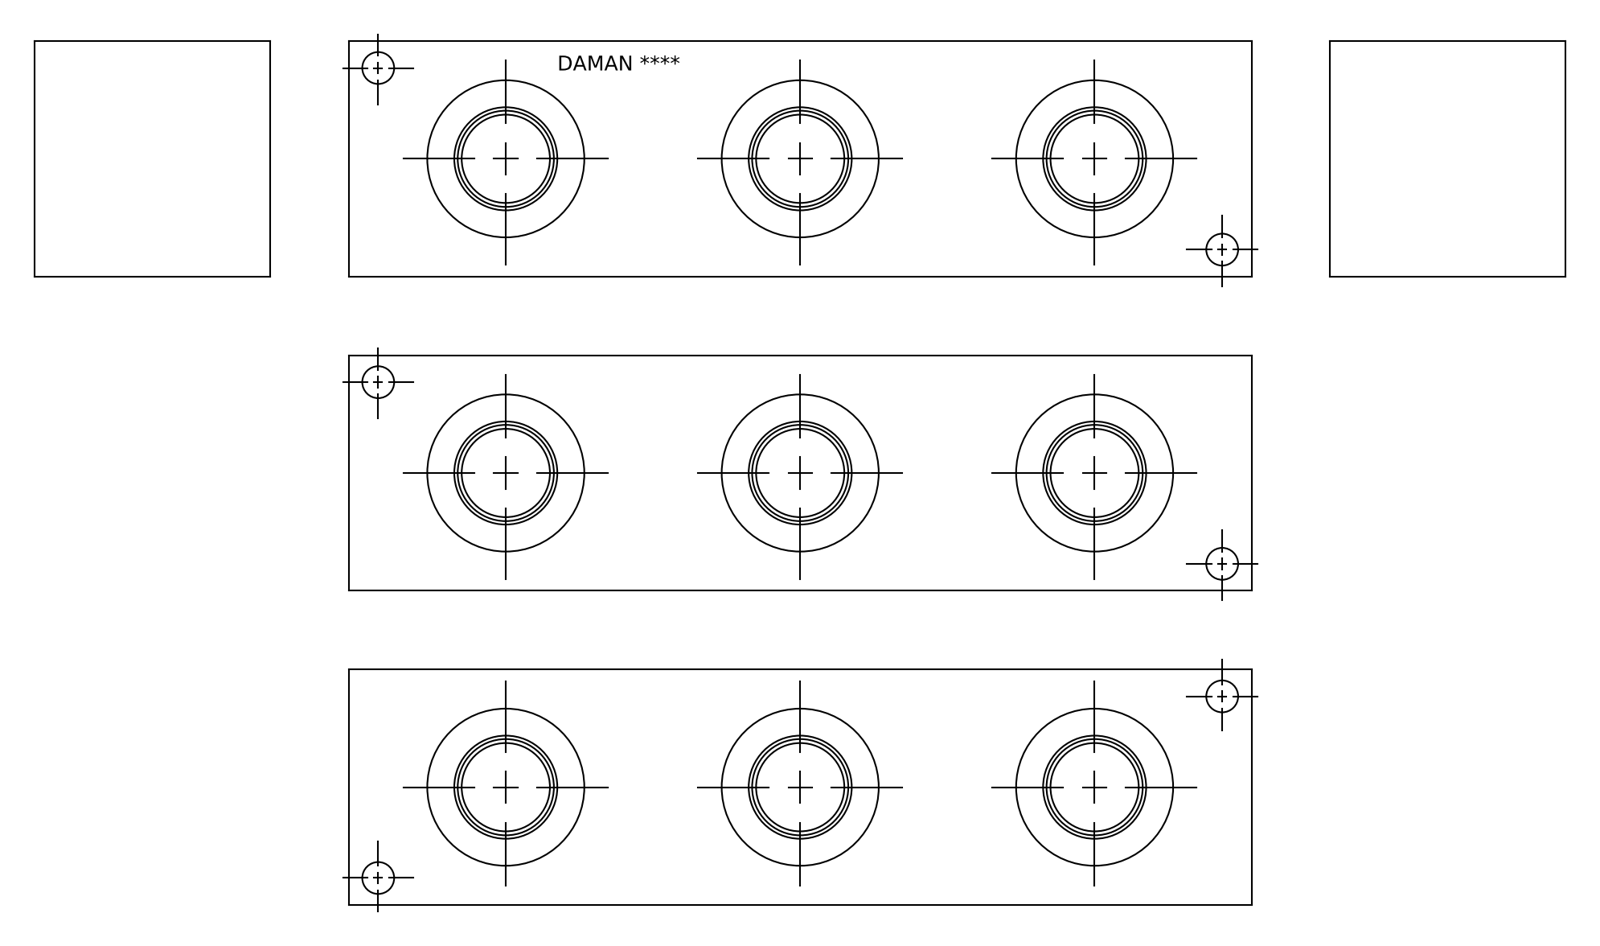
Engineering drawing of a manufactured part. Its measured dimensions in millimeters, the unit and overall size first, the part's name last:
Units: millimetres
Overall size (bounding box): 292.1 × 76.2 × 76.2
Round holes (diameter × count): ⌀28.57 ×6, ⌀31.27 ×6, ⌀33.35 ×6, ⌀33.76 ×6, ⌀35.51 ×6, ⌀49.12 ×6, ⌀10.31 ×4, ⌀33.34 ×1
Main face-to-face distances: 76.2, 0.79, 75.41, 292.1, 74.62, 19.84, 19.05, 56.36, 55.57, 36.52
Hole centre spacings: 50.65, 95.25, 139.64, 233.62, 190.5, 279.28
Volume: 1 424 000 mm³ · Surface area: 132 255 mm²
Bodies: 1 solid, 470 faces (234 planar, 64 cylindrical, 172 other)
Part name (STEP PRODUCT): Part_+J2700316S_3D
STEP written by: Autodesk Inventor 2020 (AUTOMOTIVE_DESIGN)
